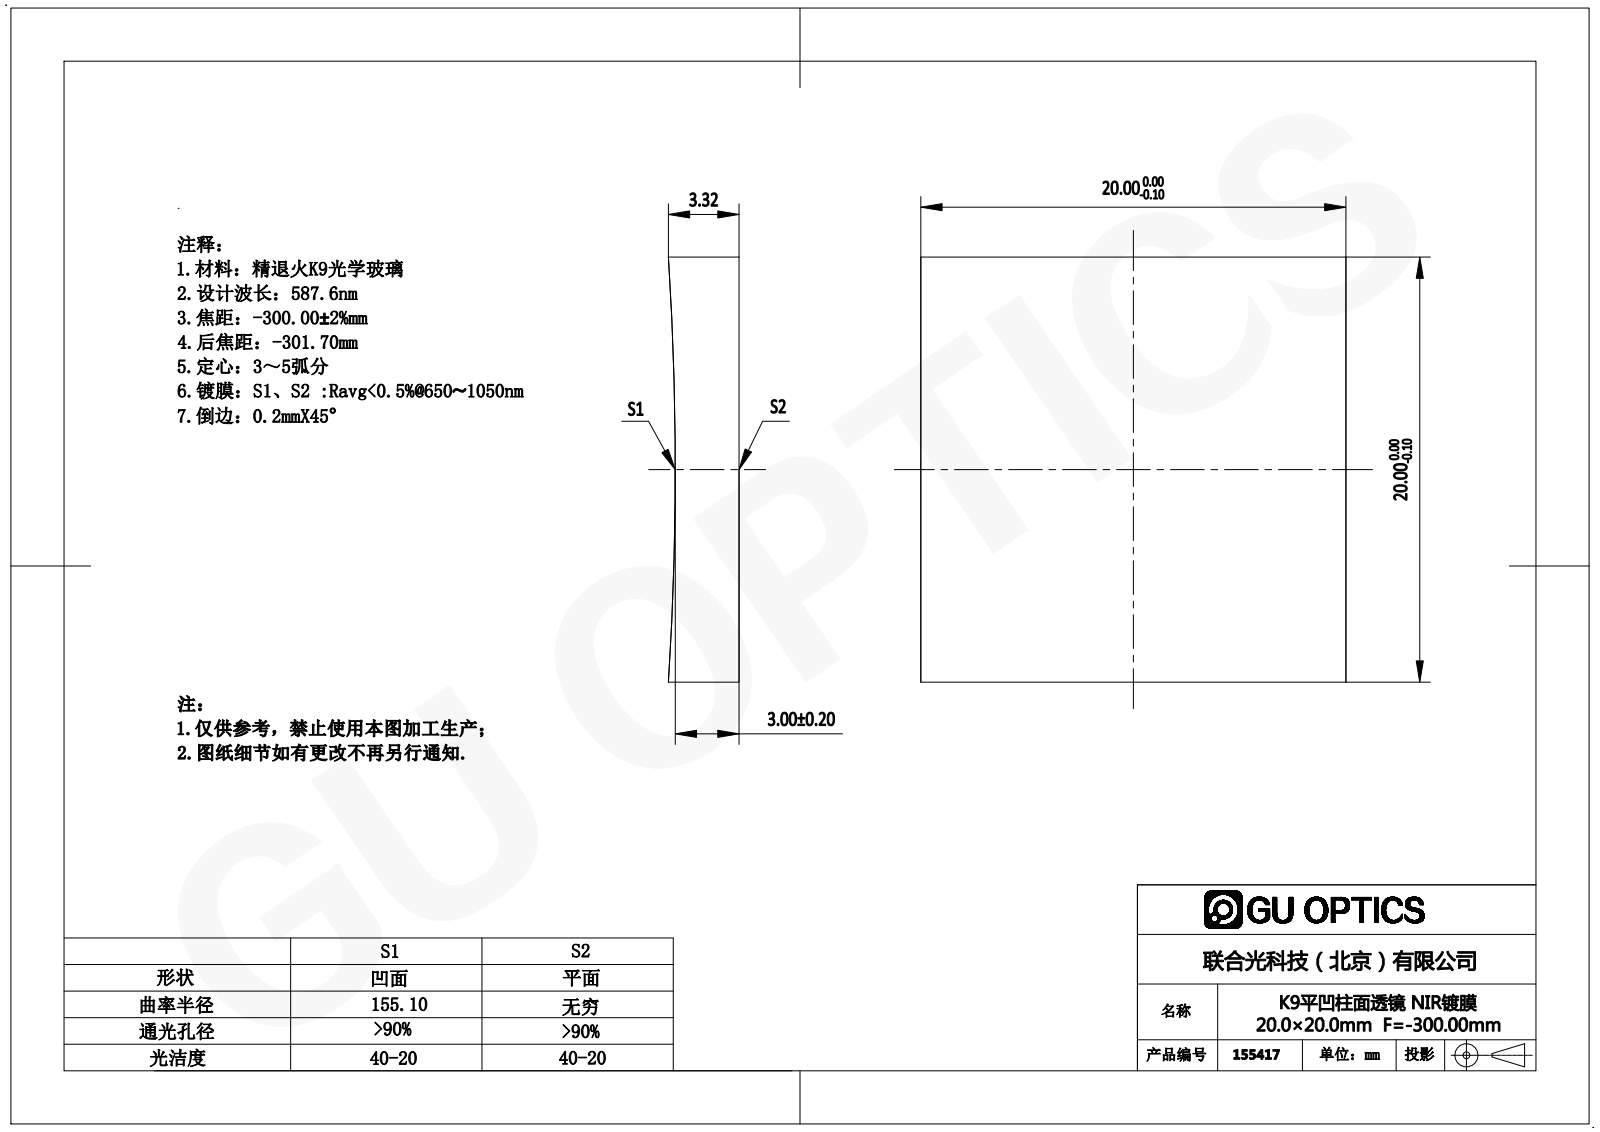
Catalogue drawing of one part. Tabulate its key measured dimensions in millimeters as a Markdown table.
| quantity | value |
| --- | --- |
| part name | 155351 |
| STEP written by | SolidWorks 2016 (AUTOMOTIVE_DESIGN) |
| units | millimeters |
| bodies | 1 solid, 6 faces (5 planar, 1 cylindrical, 0 other) |
| overall size | 20 × 20 × 3.32 |
| volume | 1 243 mm³ |
| surface area | 1 057 mm² |
| partial cylindrical surfaces (radius × count) | 155.1 × 1 |
| main face-to-face distances | 20 |
